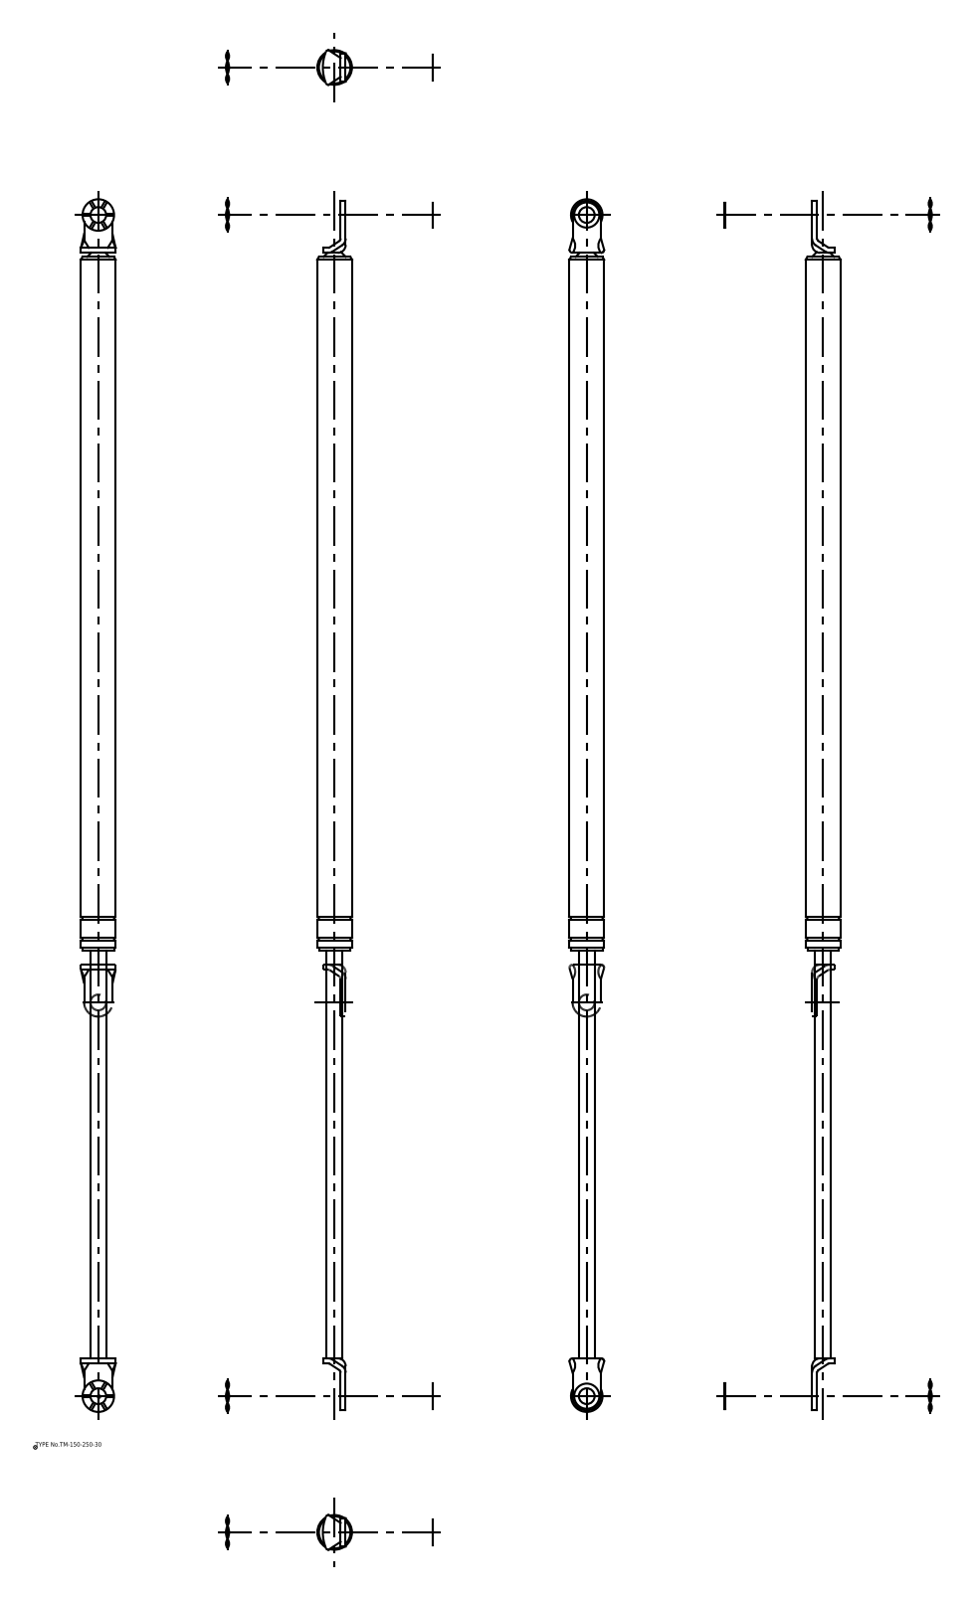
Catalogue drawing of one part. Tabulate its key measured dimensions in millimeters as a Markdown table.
| quantity | value |
| --- | --- |
| part name | ウェーブワッシャー; ワッシャー; 本体; 本体_div |
| STEP written by | spGate 16.7.1 (AUTOMOTIVE_DESIGN) |
| units | millimeters |
| bodies | 6 solids, 94 faces (42 planar, 44 cylindrical, 8 other) |
| overall size | 770 × 22.5 × 22.5 |
| volume | 193 590 mm³ |
| surface area | 45 081 mm² |
| round holes (diameter × count) | 10 × 2 |
| round bosses / shafts (diameter × count) | 20 × 3, 16 × 2, 22.5 × 1, 22 × 1, 10 × 1 |
| partial cylindrical surfaces (radius × count) | 4.4 × 2, 5 × 2, 9 × 2, 26.32 × 1 |
| main face-to-face distances | 3.2, 2, 5.2, 705.2, 5.7, 3.7, 0.5, 446.2, 262.2, 708.4 |
| hole center spacings | 750 |
